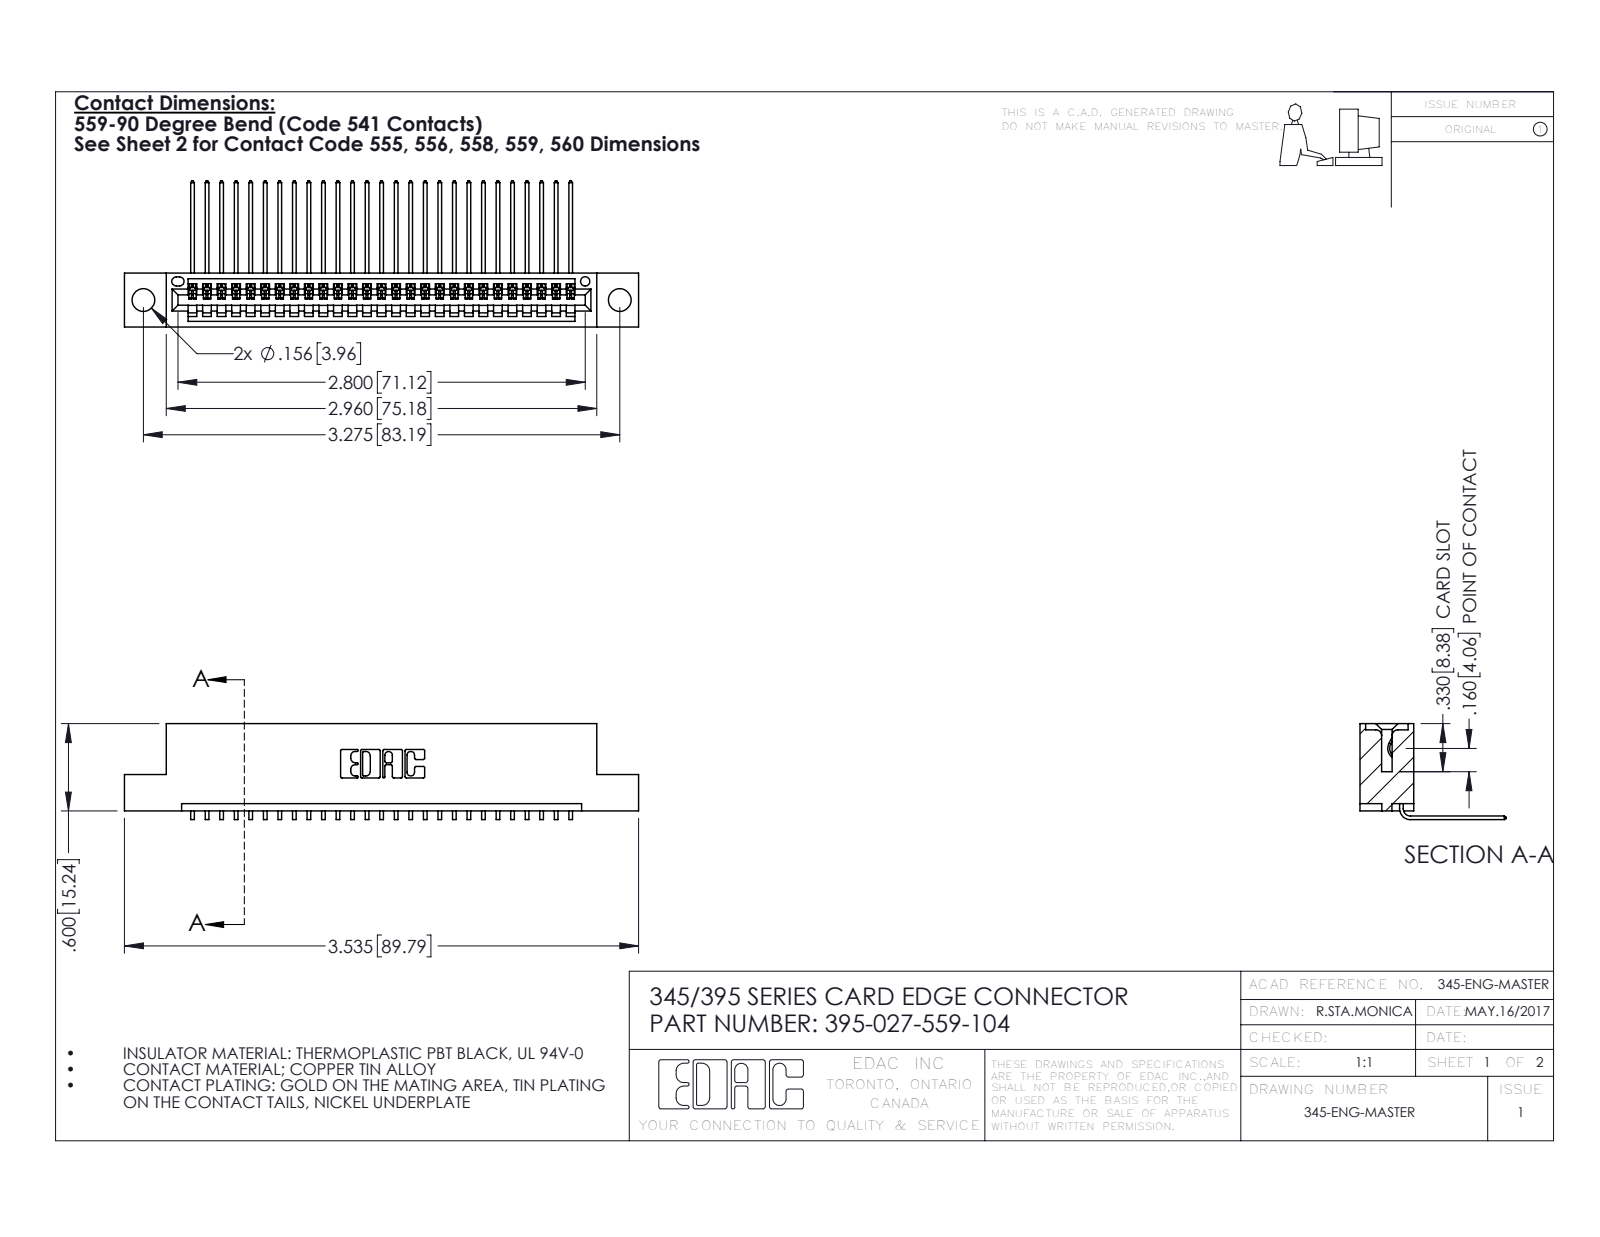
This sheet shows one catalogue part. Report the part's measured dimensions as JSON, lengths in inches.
{"part_name": "345 Part_Flush Mounting Lugs - 0.156 Dia-TH; 345-292-001_558 559 Tail - 1; 395-027-559-104", "step_written_by": "SolidWorks 2016 (CONFIG_CONTROL_DESIGN)", "units": "inches", "bodies": {"solids": 28, "faces": 1746, "planar": 1214, "cylindrical": 532, "other": 0}, "overall_size": [3.535, 1.005, 0.659], "volume_in3": 0.513, "surface_area_in2": 17.52, "round_holes": [[0.156, 2], [0.064, 1]], "partial_cylinders_radius": [[0.006, 54], [0.01, 22], [0.007, 6], [0.031, 6], [0.026, 3], [0.031, 2], [0.04, 2], [0.014, 1]], "face_to_face_distances": [0.298, 0.072, 0.37, 0.2, 0.098, 0.272, 0.025, 0.225, 0.149, 0.072], "hole_center_spacings": [0.27, 3.04, 3.275]}
